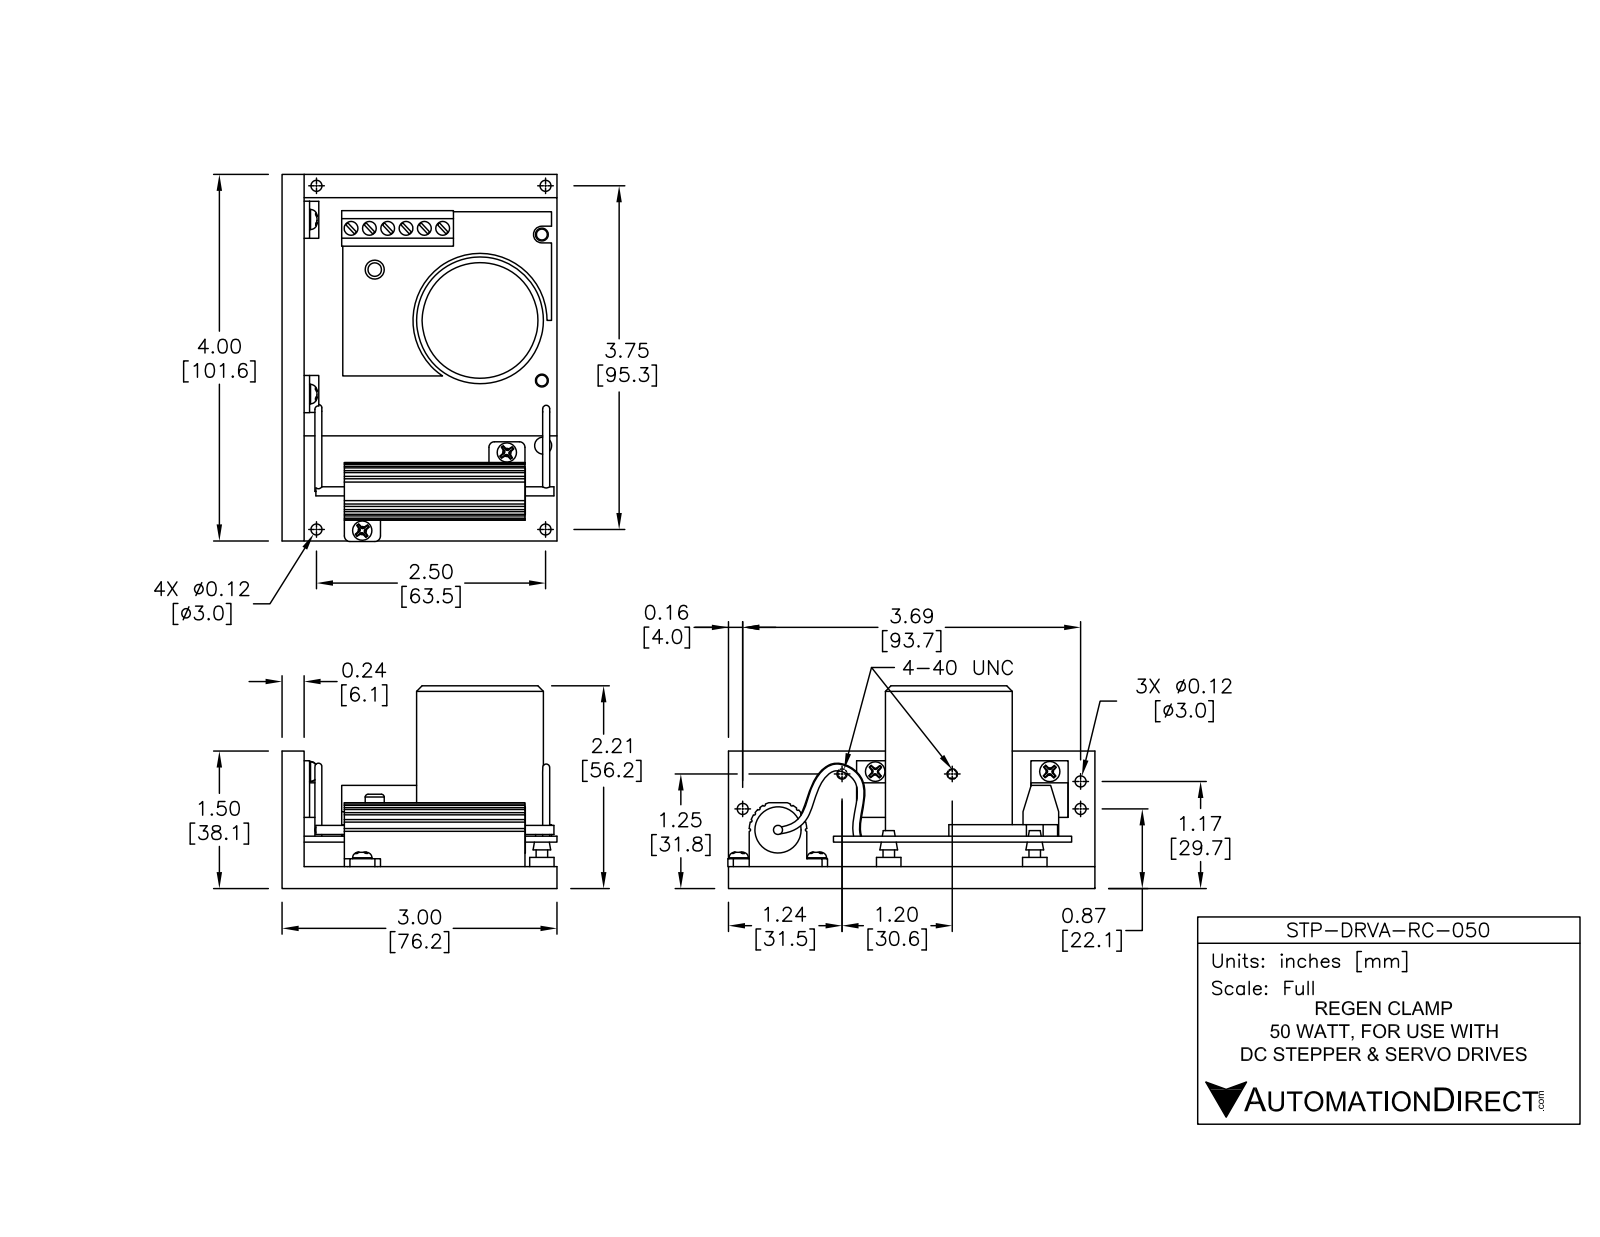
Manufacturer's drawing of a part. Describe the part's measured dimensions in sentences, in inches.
The part is named "STP-DRVA-RC-050". Its 3-D file was written by "SolidWorks 2013 (AUTOMOTIVE_DESIGN)". It is 1 solid with 350 faces: 219 planar, 89 cylindrical and 42 other. Overall it measures 4.006 by 3 by 2.212 inches. Its volume is 8.366 cubic inches and its surface area 68.86 square inches. Round holes: 7 of diameter 0.12, 6 of diameter 0.15, 2 of diameter 0.089, 1 of diameter 0.186. Round bosses or shafts: 2 of diameter 0.267, 2 of diameter 0.21, 1 of diameter 1.384, 1 of diameter 0.504, 1 of diameter 0.22, 1 of diameter 0.212, 1 of diameter 0.207, 1 of diameter 0.125. Partial cylindrical surfaces (rounded edges, fillets, slot ends): 10 of radius 0.015, 4 of radius 0.06, 1 of radius 0.091, 1 of radius 0.314, 1 of radius 0.731. The main face-to-face distances are 0.24, 0.507, 0.267, 0.065, 0.572, 0.332, 0.457, 0.125, 0.697, 0.19. The hole center spacings are 0.2, 0.4, 0.6, 0.8, 2.5, 3.75, 4.507, 0.3.
